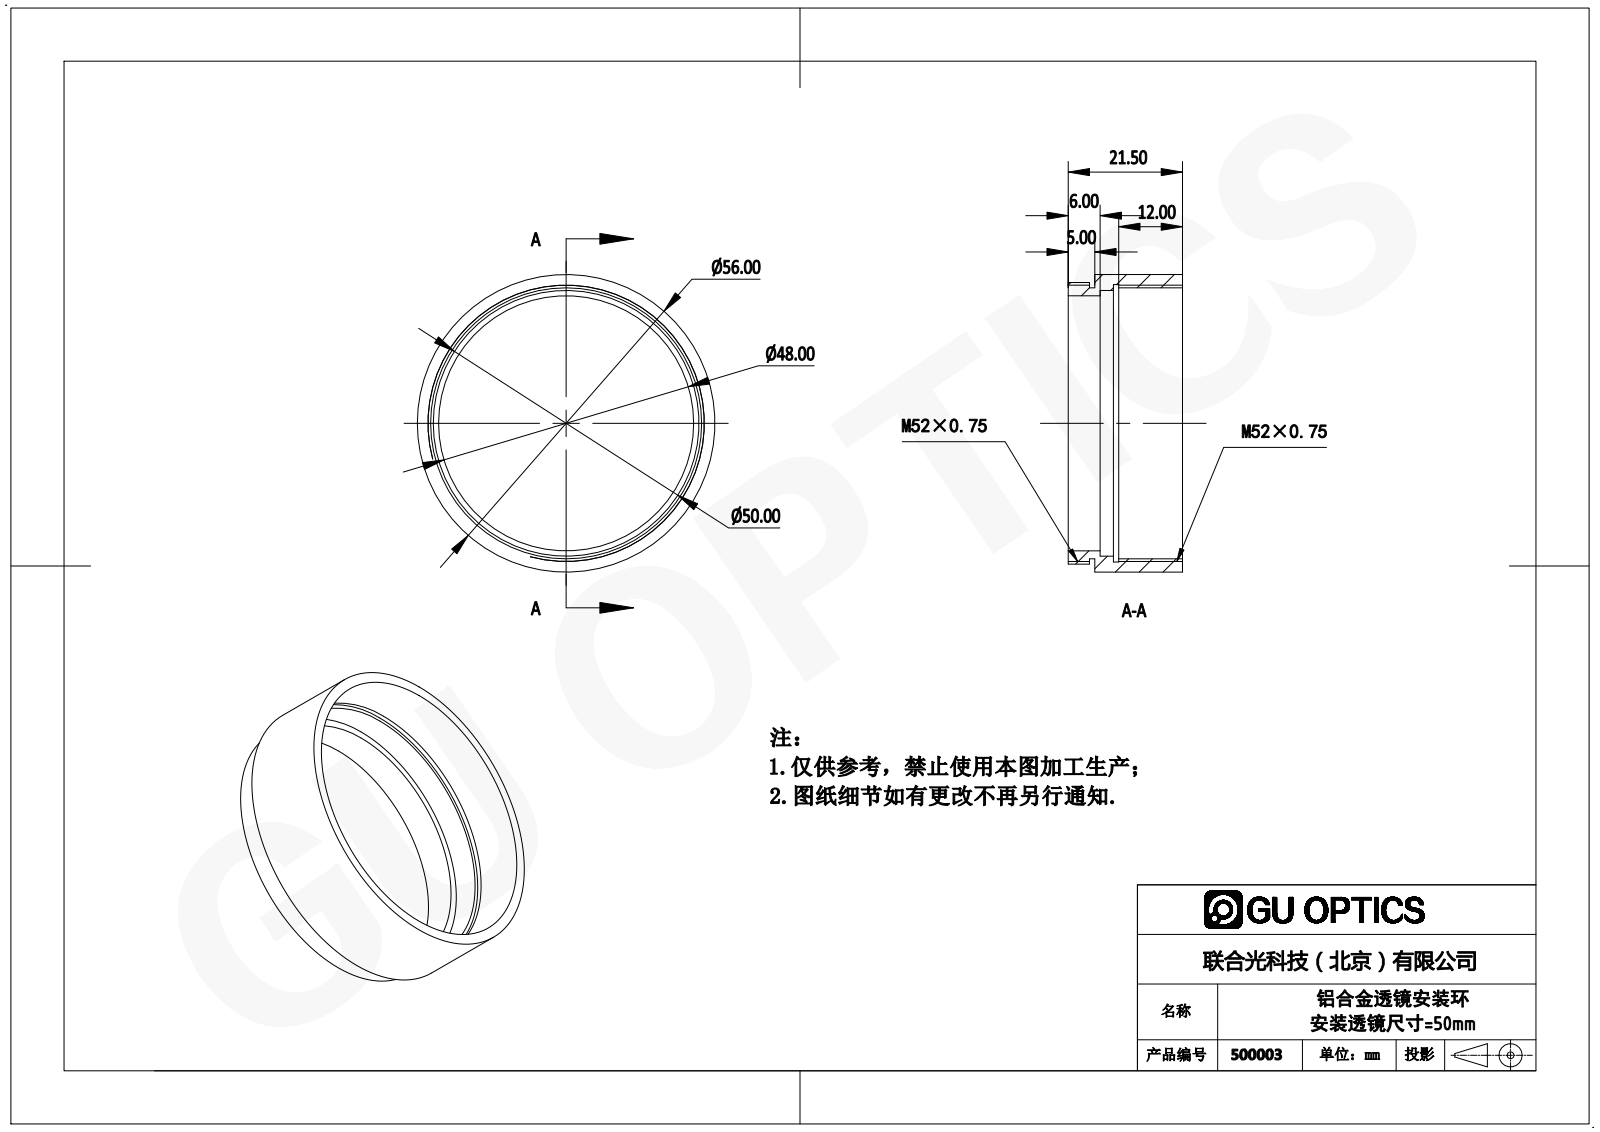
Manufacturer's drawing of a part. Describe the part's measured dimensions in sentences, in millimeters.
The part is named "500003". Its 3-D file was written by "SolidWorks 2016 (AUTOMOTIVE_DESIGN)". It is 1 solid with 21 faces: 7 planar, 14 cylindrical and 0 other. Overall it measures 56 by 56 by 21.5 millimeters. Its volume is 9 087 cubic millimeters and its surface area 8 941 square millimeters. Round holes: 1 of diameter 48, 1 of diameter 50, 1 of diameter 51, 1 of diameter 52.2. Round bosses or shafts: 1 of diameter 56, 1 of diameter 53. The main face-to-face distances are 16.5, 1, 5, 21.5, 3.5, 4.5, 8.5, 13, 4, 17.5.
